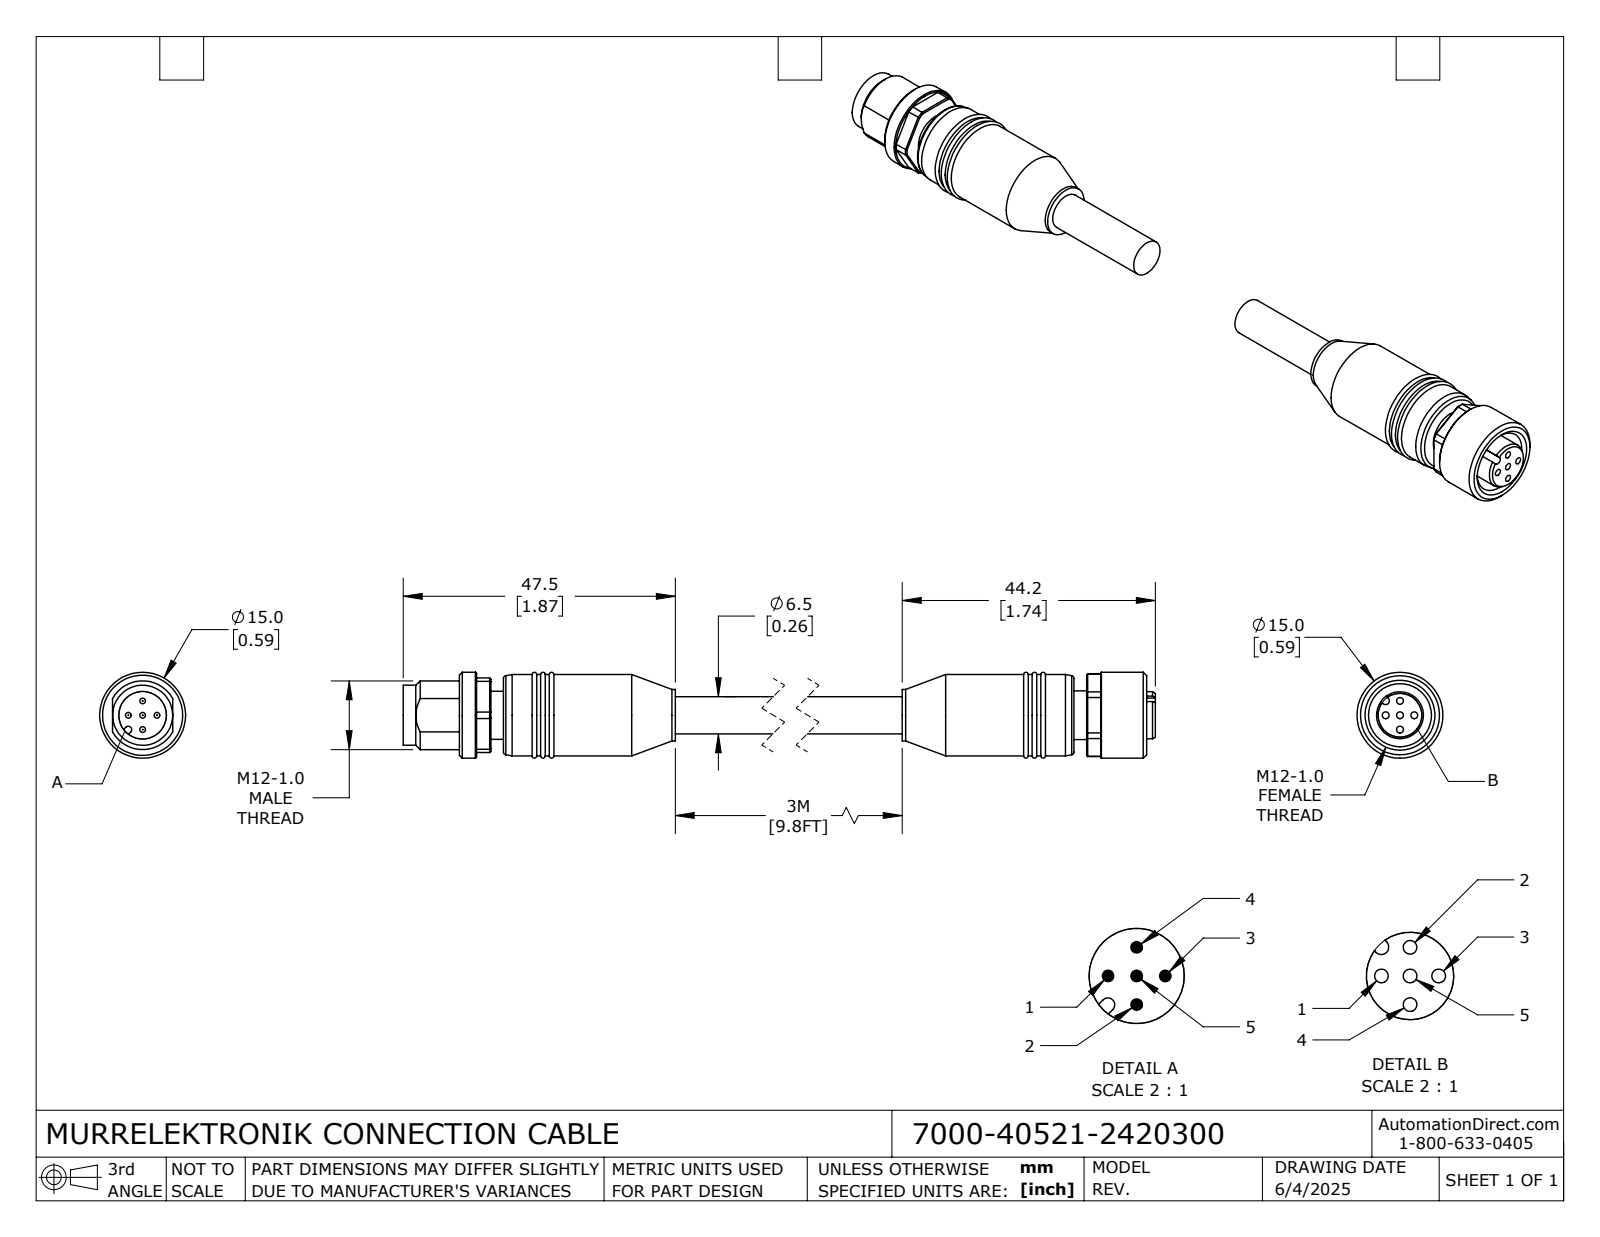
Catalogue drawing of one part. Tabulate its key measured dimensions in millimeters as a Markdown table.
| quantity | value |
| --- | --- |
| part name | 7000-40521-2420300; 7000-40521-2420300_FEMALE; 7000-40521-2420300_MALE |
| STEP written by | SolidWorks 2024 (CONFIG_CONTROL_DESIGN) |
| units | millimeters |
| bodies | 2 solids, 198 faces (58 planar, 77 cylindrical, 63 other) |
| overall size | 156.7 × 15 × 15 |
| volume | 13 209 mm³ |
| surface area | 6 539 mm² |
| round holes (diameter × count) | 1.2 × 5, 8.3 × 1, 11 × 1 |
| round bosses / shafts (diameter × count) | 1 × 5, 15 × 1, 14.2 × 1, 10.5 × 1, 9 × 1, 8.5 × 1, 8.4 × 1, 8.2 × 1 |
| partial cylindrical surfaces (radius × count) | 0.6 × 1, 0.65 × 1, 6 × 1, 7.2 × 1 |
| main face-to-face distances | 2.2, 127.2, 13, 129.4, 10.5, 125, 134.9, 52.2, 77.2, 50 |
| hole center spacings | 2.5, 3.54, 5 |
